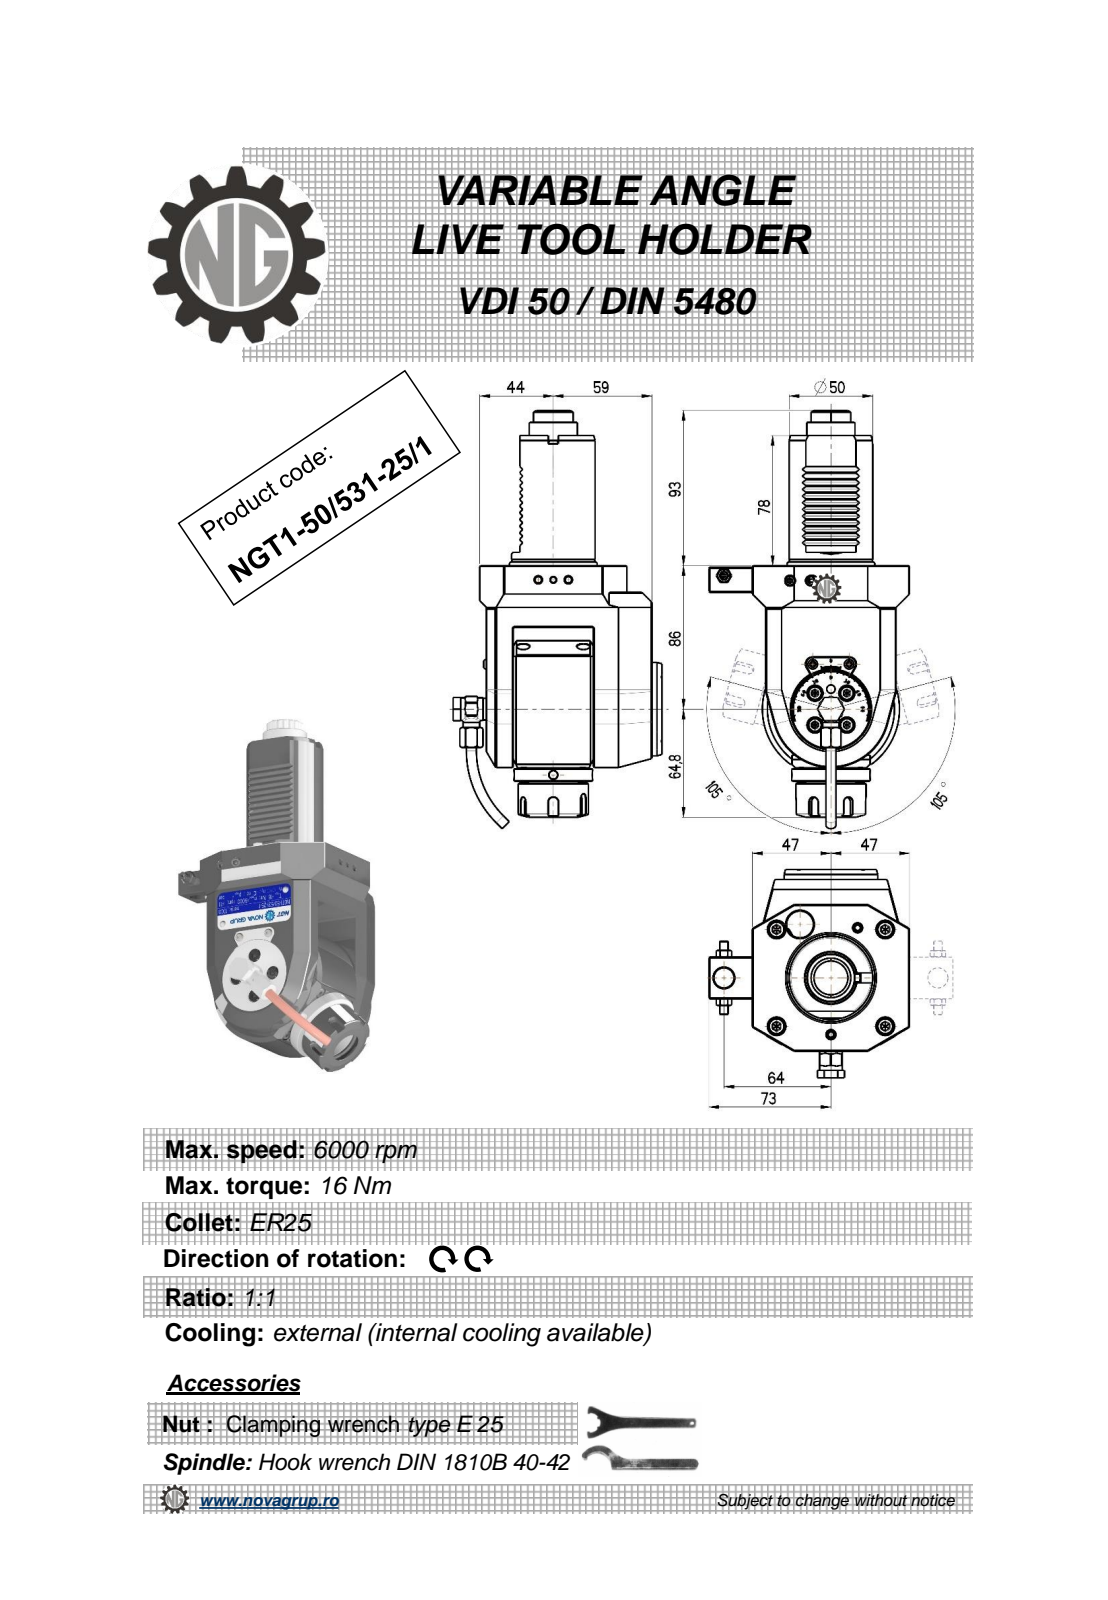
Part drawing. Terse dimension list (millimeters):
name: NGT1_50_531_25_1
written by: PRO/ENGINEER BY PARAMETRIC TECHNOLOGY CORPORATION, 2010280 (CONFIG_CONTROL_DESIGN)
unit: mm
bodies: 1 solid, 700 faces (265 planar, 209 cylindrical, 226 other)
size: 250.67 × 124.9 × 120
volume: 1 025 000 mm³; area: 91 332 mm²
holes: 3× ⌀4, 2× ⌀5, 1× ⌀3, 1× ⌀4.2, 1× ⌀6.2, 1× ⌀9, 1× ⌀9.5, 1× ⌀10, 1× ⌀11, 1× ⌀12, 1× ⌀20.3
bosses: 2× ⌀6, 2× ⌀5.7, 1× ⌀82, 1× ⌀56, 1× ⌀50, 1× ⌀47, 1× ⌀42, 1× ⌀35
rounds: 36× R3.04, 12× R0.26, 12× R0.3, 6× R0.16, 5× R3, 4× R0.5, 2× R1, 2× R10
face distances: 37, 99, 16, 78, 8, 20, 6, 64, 105, 21
hole spacings: 0.4, 39.45, 49, 49.4, 64, 80.6, 80.85, 102.45
